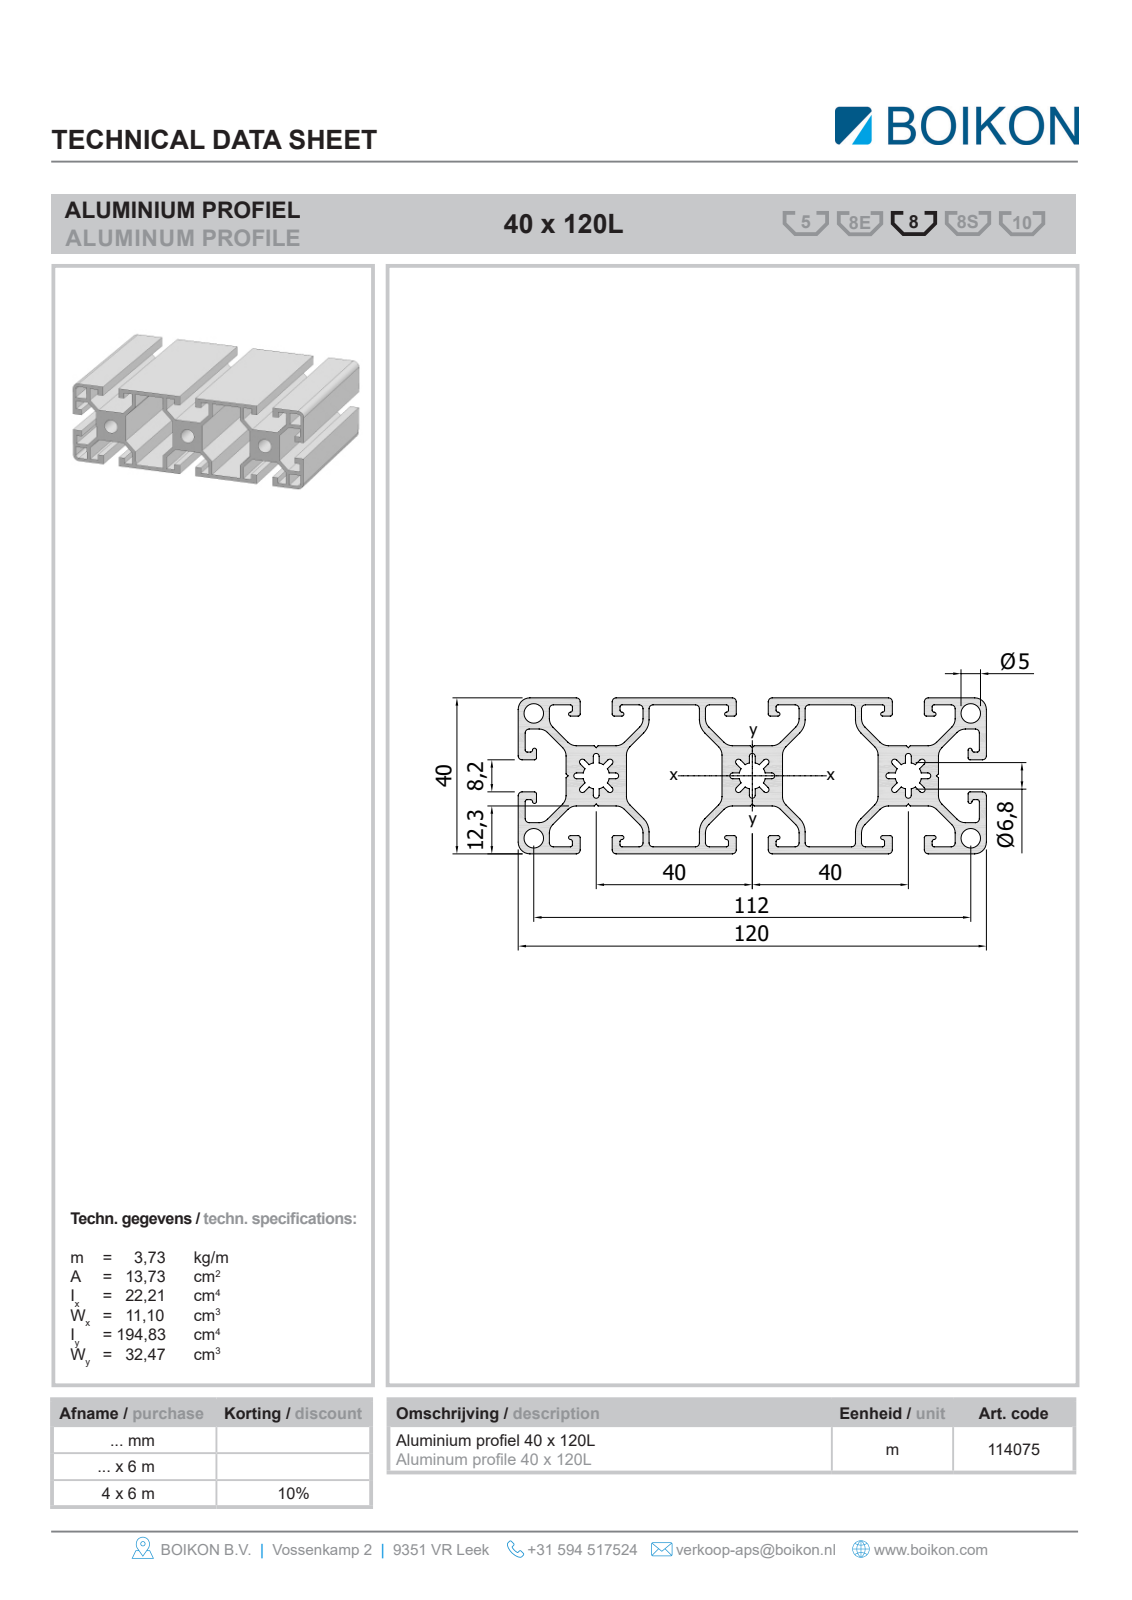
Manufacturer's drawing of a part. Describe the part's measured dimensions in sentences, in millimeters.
The part is named "Root; 11407540x120LBOIKON0". Its 3-D file was written by "HiCAD 2013 1802.4 Build 509 (AUTOMOTIVE_DESIGN)". It is 1 solid with 169 faces: 158 planar, 11 cylindrical and 0 other. Overall it measures 1000 by 120 by 40 millimeters. Its volume is 1 463 000 cubic millimeters and its surface area 1 152 000 square millimeters. Round holes: 3 of diameter 6.8. Partial cylindrical surfaces (rounded edges, fillets, slot ends): 4 of radius 1.5, 4 of radius 3. The main face-to-face distances are 1.8, 40, 38.2, 28.28, 27.7, 12.3, 5.1, 20.5, 3.3, 18.7. The hole center spacings are 40, 80.
